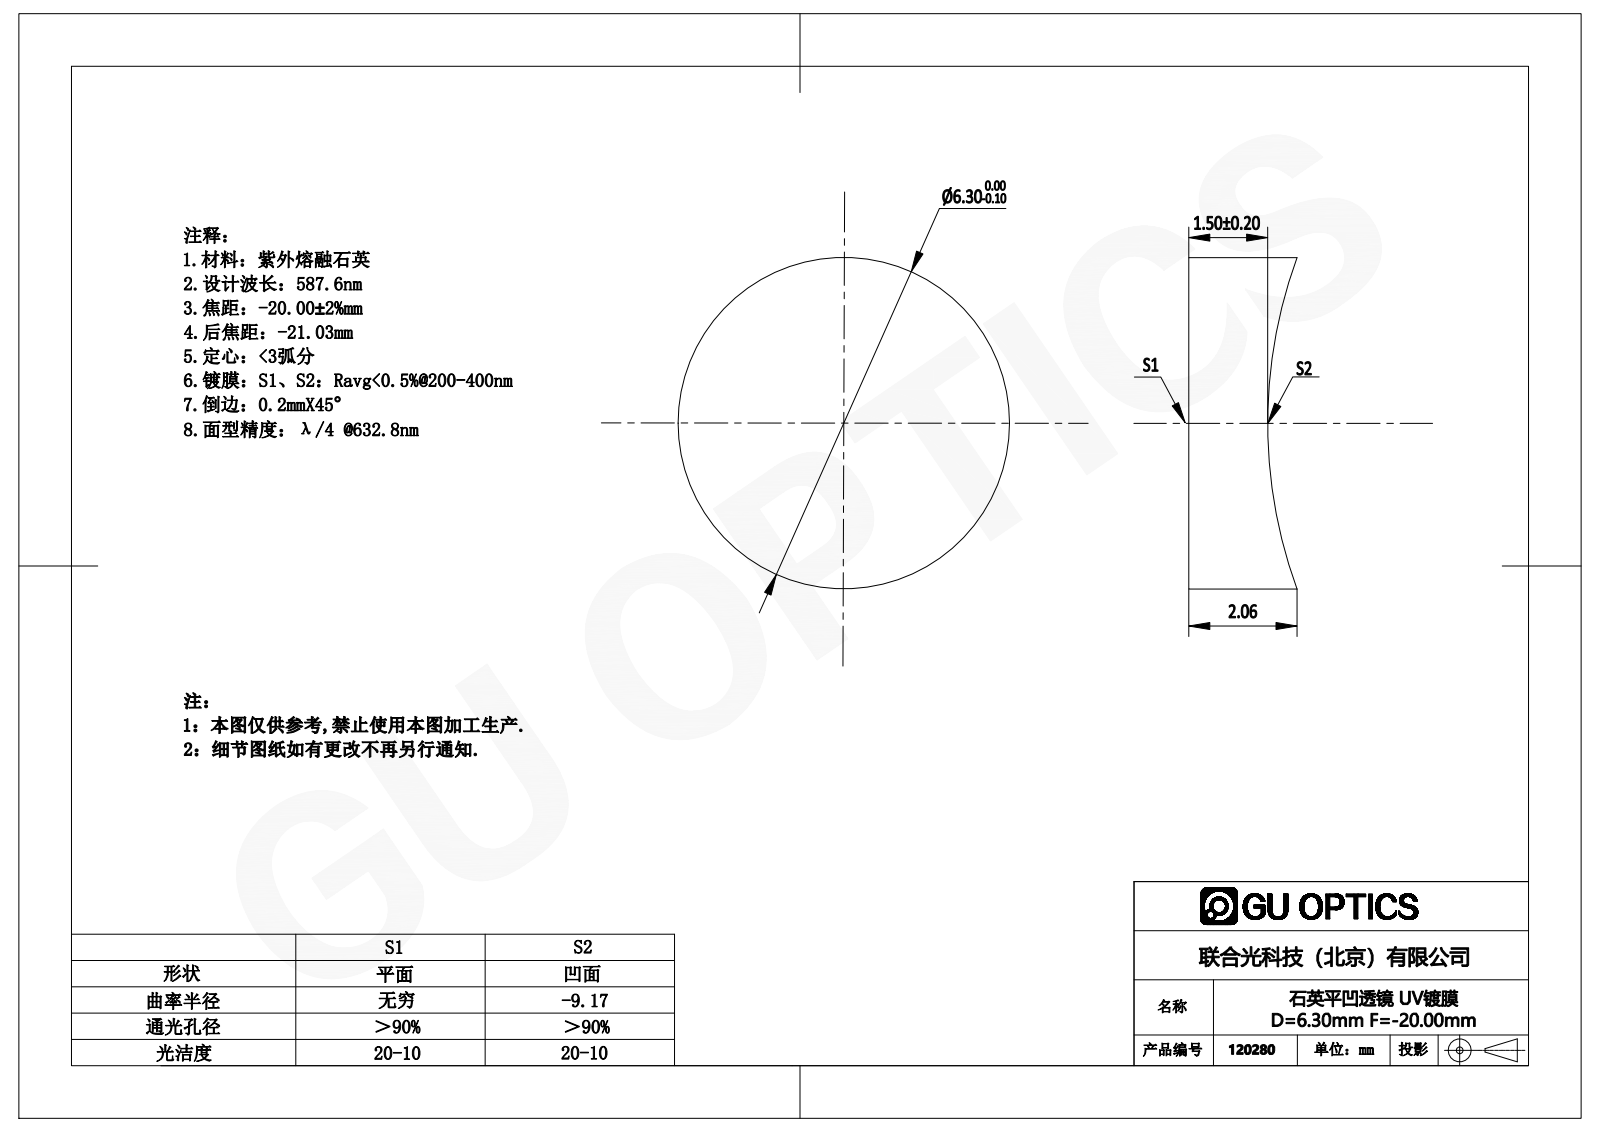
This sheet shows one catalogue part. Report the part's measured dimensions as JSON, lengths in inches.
{"part_name": "120247", "step_written_by": "SolidWorks 2016 (AUTOMOTIVE_DESIGN)", "units": "inches", "bodies": {"solids": 1, "faces": 5, "planar": 1, "cylindrical": 2, "other": 2}, "overall_size": [0.248, 0.248, 0.081], "volume_in3": 0.003, "surface_area_in2": 0.161, "round_bosses_or_shafts": [[0.248, 1]]}
